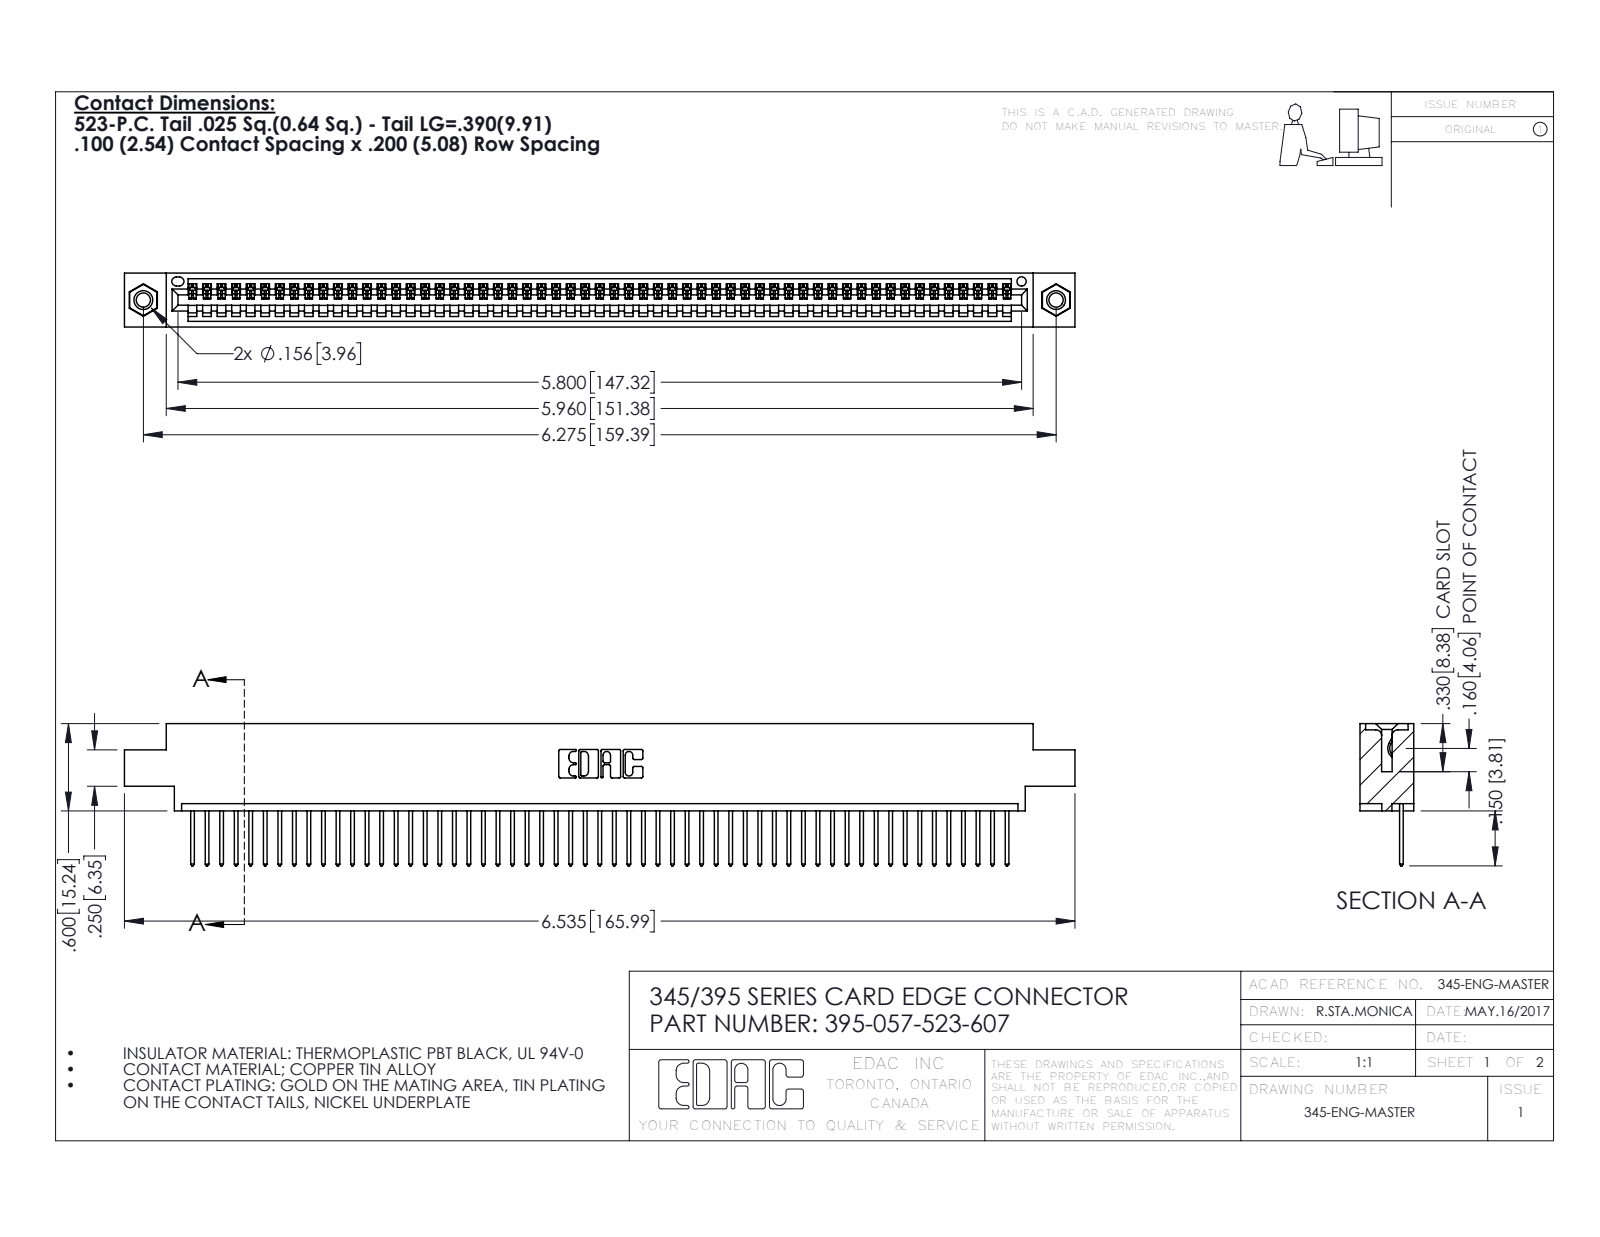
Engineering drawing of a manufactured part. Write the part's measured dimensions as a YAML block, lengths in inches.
part_name: "395-057-523-607; 345 Part_0.170 Offset - 0.156 Dia-TI; 345-250-001_345-250-005-103; 345-292-001_345-293-123"
step_written_by: "SolidWorks 2016 (CONFIG_CONTROL_DESIGN)"
units: inches
bodies: {solids: 60, faces: 3496, planar: 2396, cylindrical: 1084, other: 16}
overall_size: [6.535, 0.977, 0.37]
volume: 0.96
surface_area: 33.08
round_holes:
  - {diameter: 0.098, count: 2}
  - {diameter: 0.125, count: 2}
  - {diameter: 0.156, count: 2}
  - {diameter: 0.064, count: 1}
round_bosses_or_shafts:
  - {diameter: 0.155, count: 2}
partial_cylinders:
  - {radius: 0.006, count: 114}
  - {radius: 0.01, count: 114}
  - {radius: 0.01, count: 22}
  - {radius: 0.007, count: 6}
  - {radius: 0.031, count: 6}
  - {radius: 0.026, count: 3}
  - {radius: 0.031, count: 2}
  - {radius: 0.04, count: 2}
face_to_face_distances: [0.072, 0.298, 0.37, 0.098, 0.272, 0.025, 0.2, 0.225, 0.175, 0.149]
hole_center_spacings: [0.27, 6.039, 6.275]
